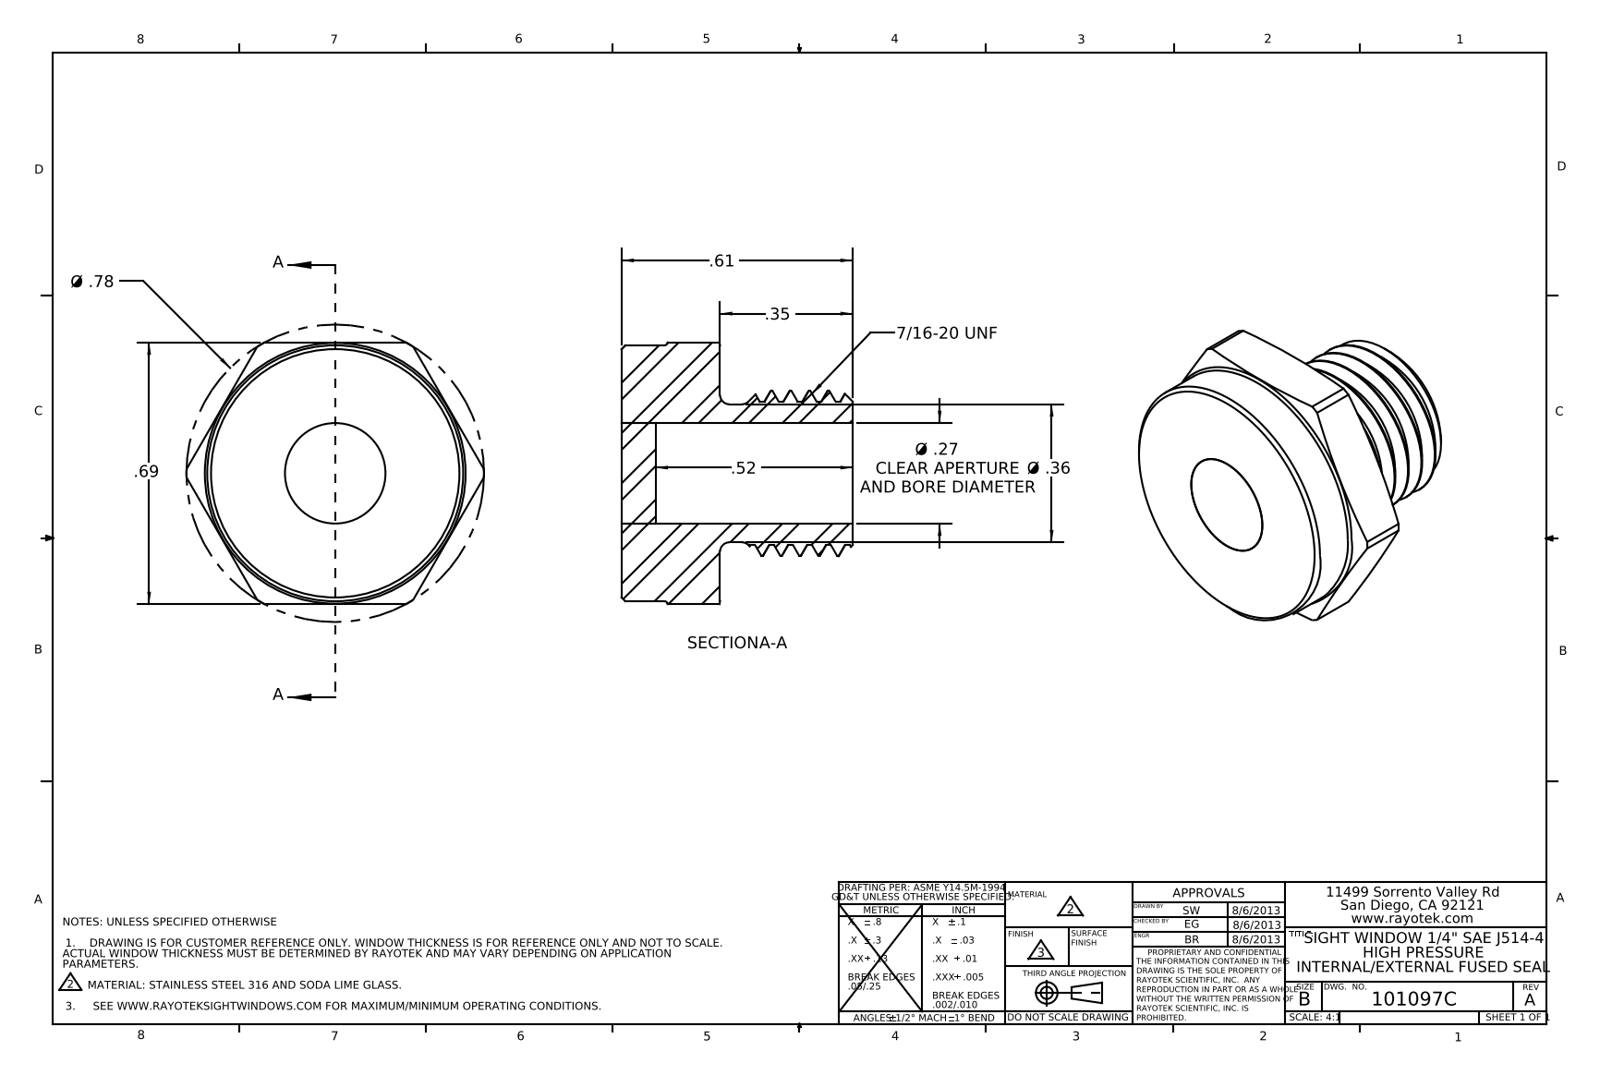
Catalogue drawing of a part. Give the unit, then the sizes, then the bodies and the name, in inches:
Units: inches
Overall size (bounding box): 0.785 × 0.69 × 0.61
Round holes (diameter × count): ⌀0.265 ×1
Round bosses / shafts (diameter × count): ⌀0.675 ×1, ⌀0.437 ×1, ⌀0.364 ×1
Partial cylindrical surfaces — rounded edges, fillets, slot ends (radius × count): R0.392 ×1
Main face-to-face distances: 0.26, 0.69, 0.35, 0.61, 0.52, 0.17, 0.09
Volume: 0.114 in³ · Surface area: 2.611 in²
Bodies: 2 solids, 56 faces (11 planar, 24 cylindrical, 21 other)
Part name (STEP PRODUCT): 403097
STEP written by: SolidWorks 2012 (AUTOMOTIVE_DESIGN)
